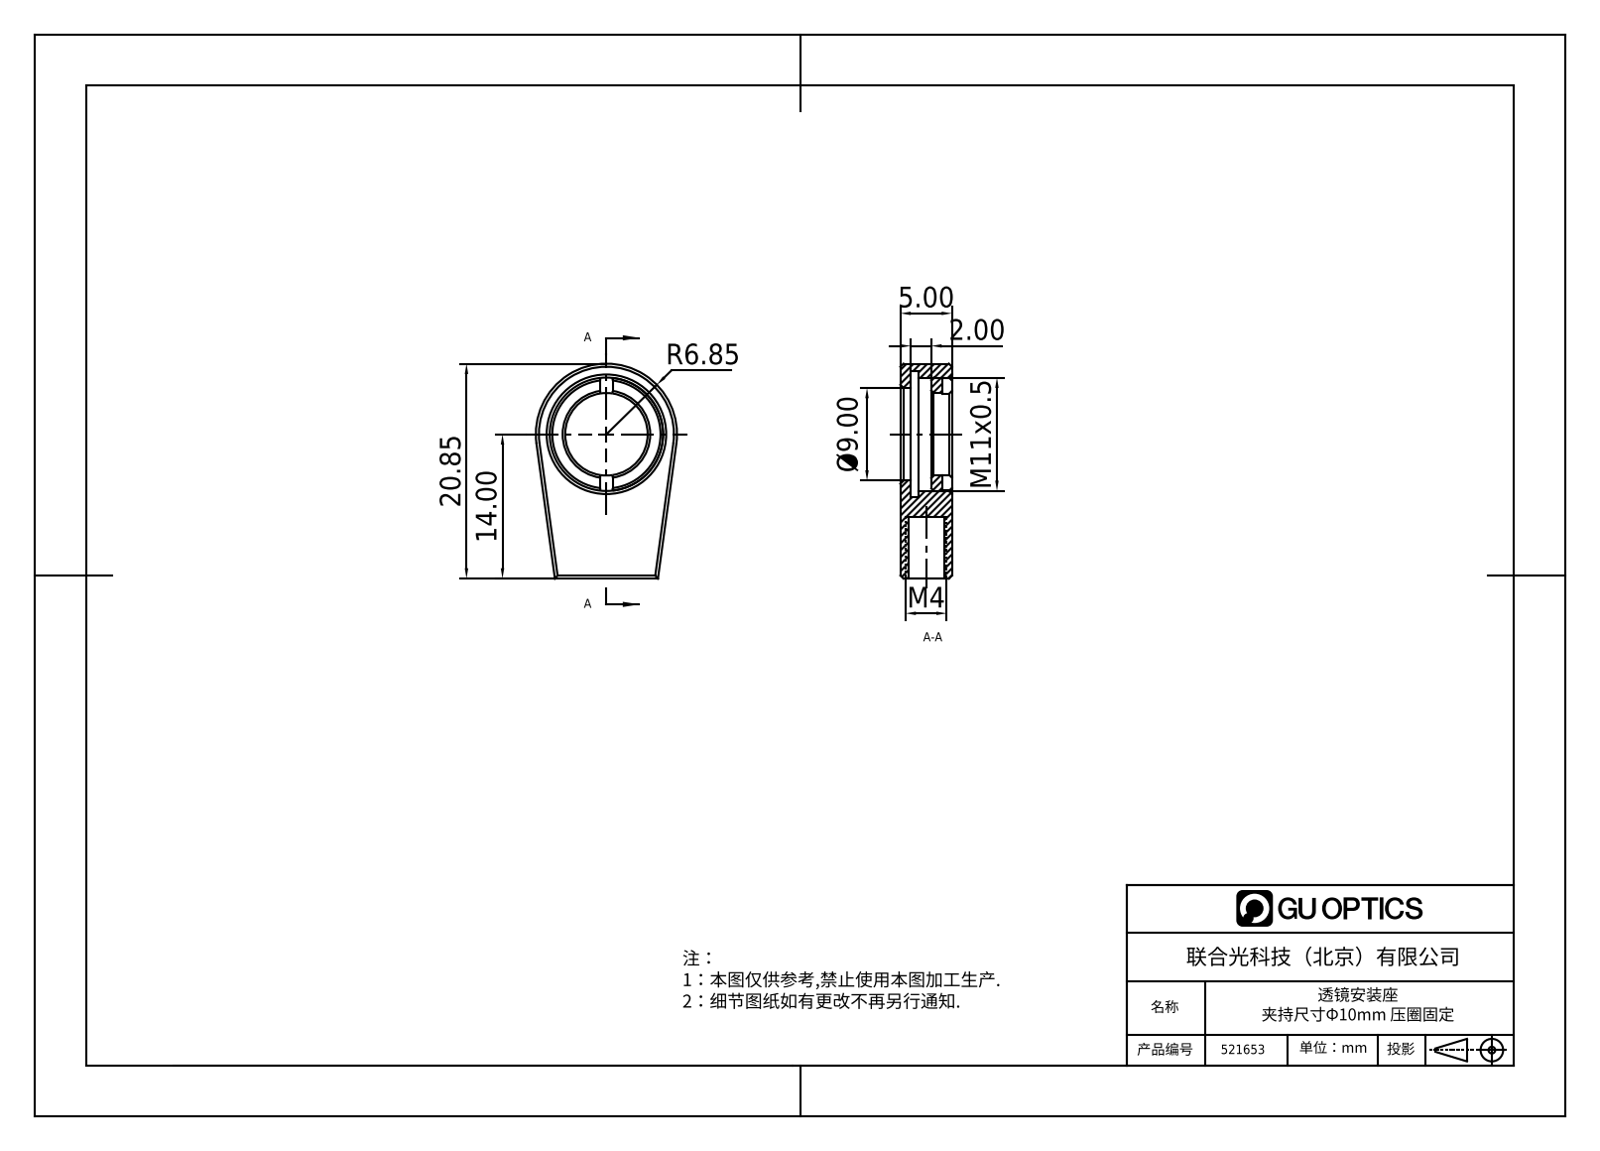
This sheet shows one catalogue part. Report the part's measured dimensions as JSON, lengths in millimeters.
{"part_name": "1.3.1.11-ZZT-10M", "step_written_by": "SolidWorks 2021 (CONFIG_CONTROL_DESIGN)", "units": "millimeters", "bodies": {"solids": 0, "faces": 59, "planar": 22, "cylindrical": 15, "other": 22}, "overall_size": [20.85, 13.7, 5], "round_holes": [[4, 1], [8, 1], [9, 1], [11, 1], [12.2, 1]], "partial_cylinders_radius": [[6.85, 1]], "face_to_face_distances": [5, 2, 1, 4, 3, 1.2, 1.8, 0.8, 3.2, 4.1]}
